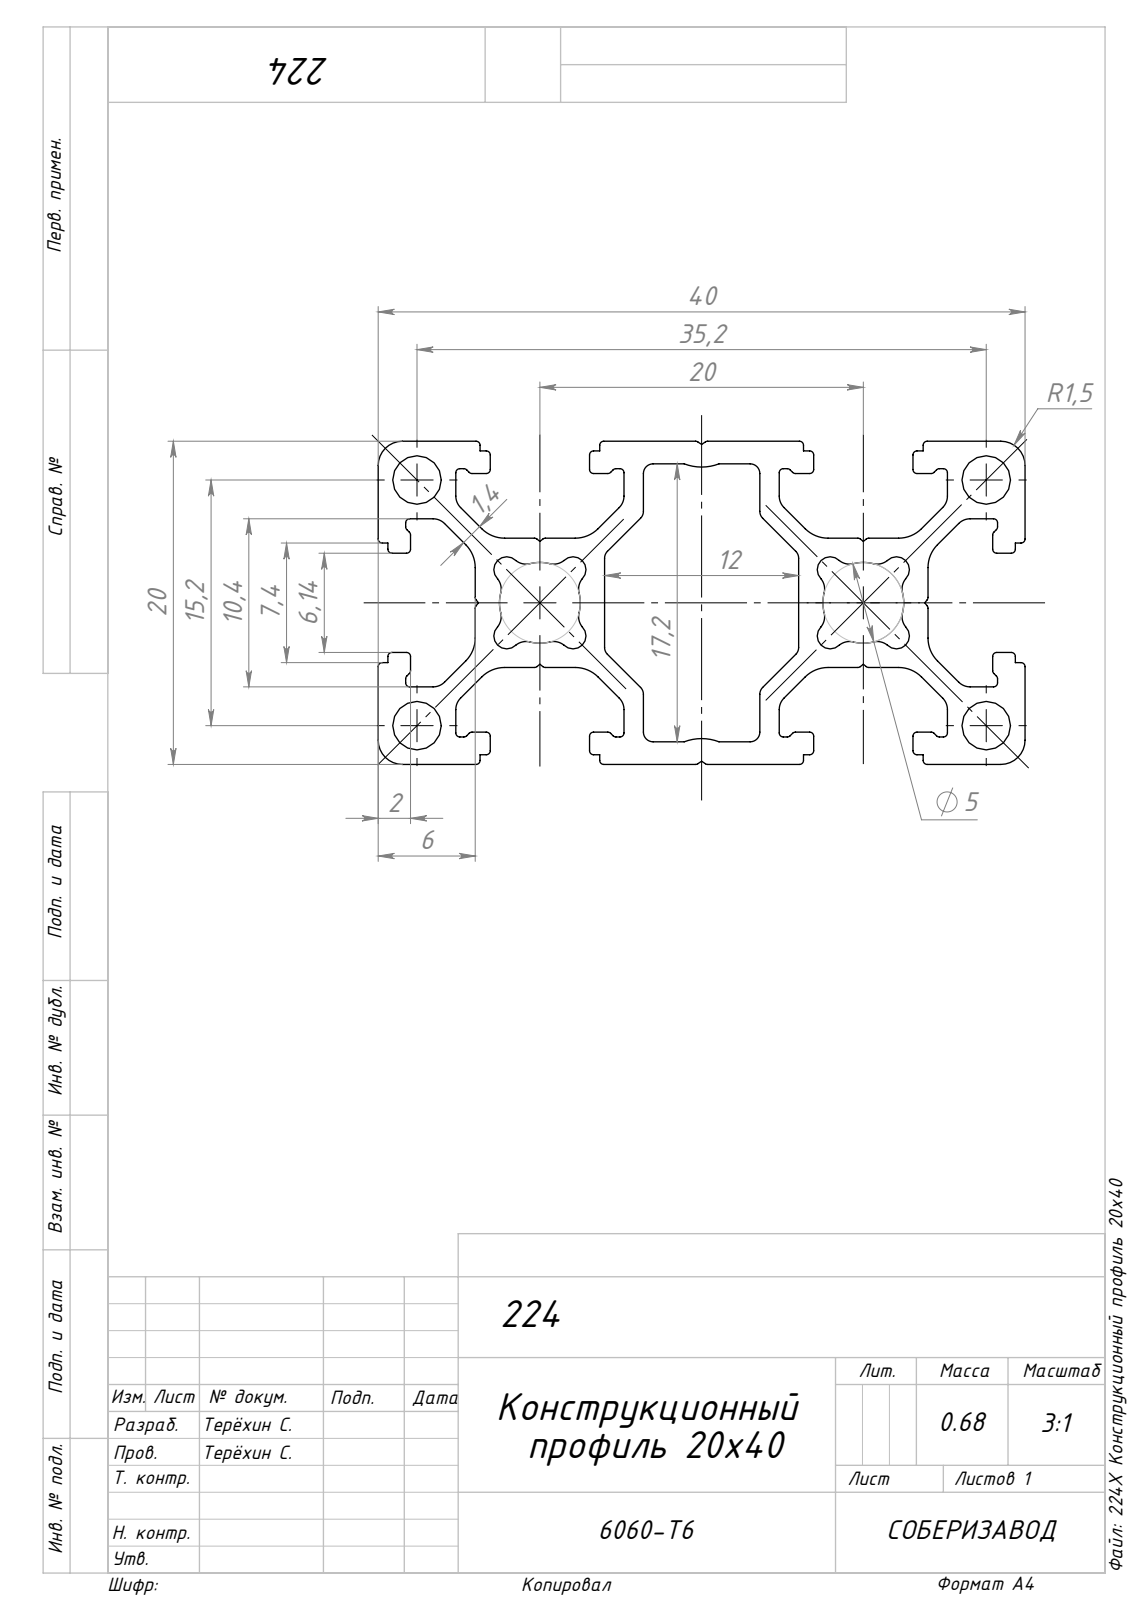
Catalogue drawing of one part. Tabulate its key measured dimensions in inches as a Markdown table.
| quantity | value |
| --- | --- |
| part name | Сборка2; 224 Конструкционный профиль 20х40_00 |
| STEP written by | SolidWorks 2022 (AUTOMOTIVE_DESIGN) |
| units | inches |
| bodies | 1 solid, 332 faces (152 planar, 180 cylindrical, 0 other) |
| overall size | 39.37 × 1.575 × 0.787 |
| volume | 15.33 in³ |
| surface area | 556.4 in² |
| round holes (diameter × count) | 0.118 × 4 |
| partial cylindrical surfaces (radius × count) | 0.01 × 88, 0.039 × 28, 0.024 × 12, 0.079 × 12, 0.031 × 8, 0.059 × 4, 0.098 × 2, 0.118 × 2 |
| main face-to-face distances | 0.787, 0.055, 0.551, 0.047, 0.236, 0.472, 0.362, 0.409, 0.557, 0.315 |
| hole center spacings | 0.598, 1.386, 1.509 |
